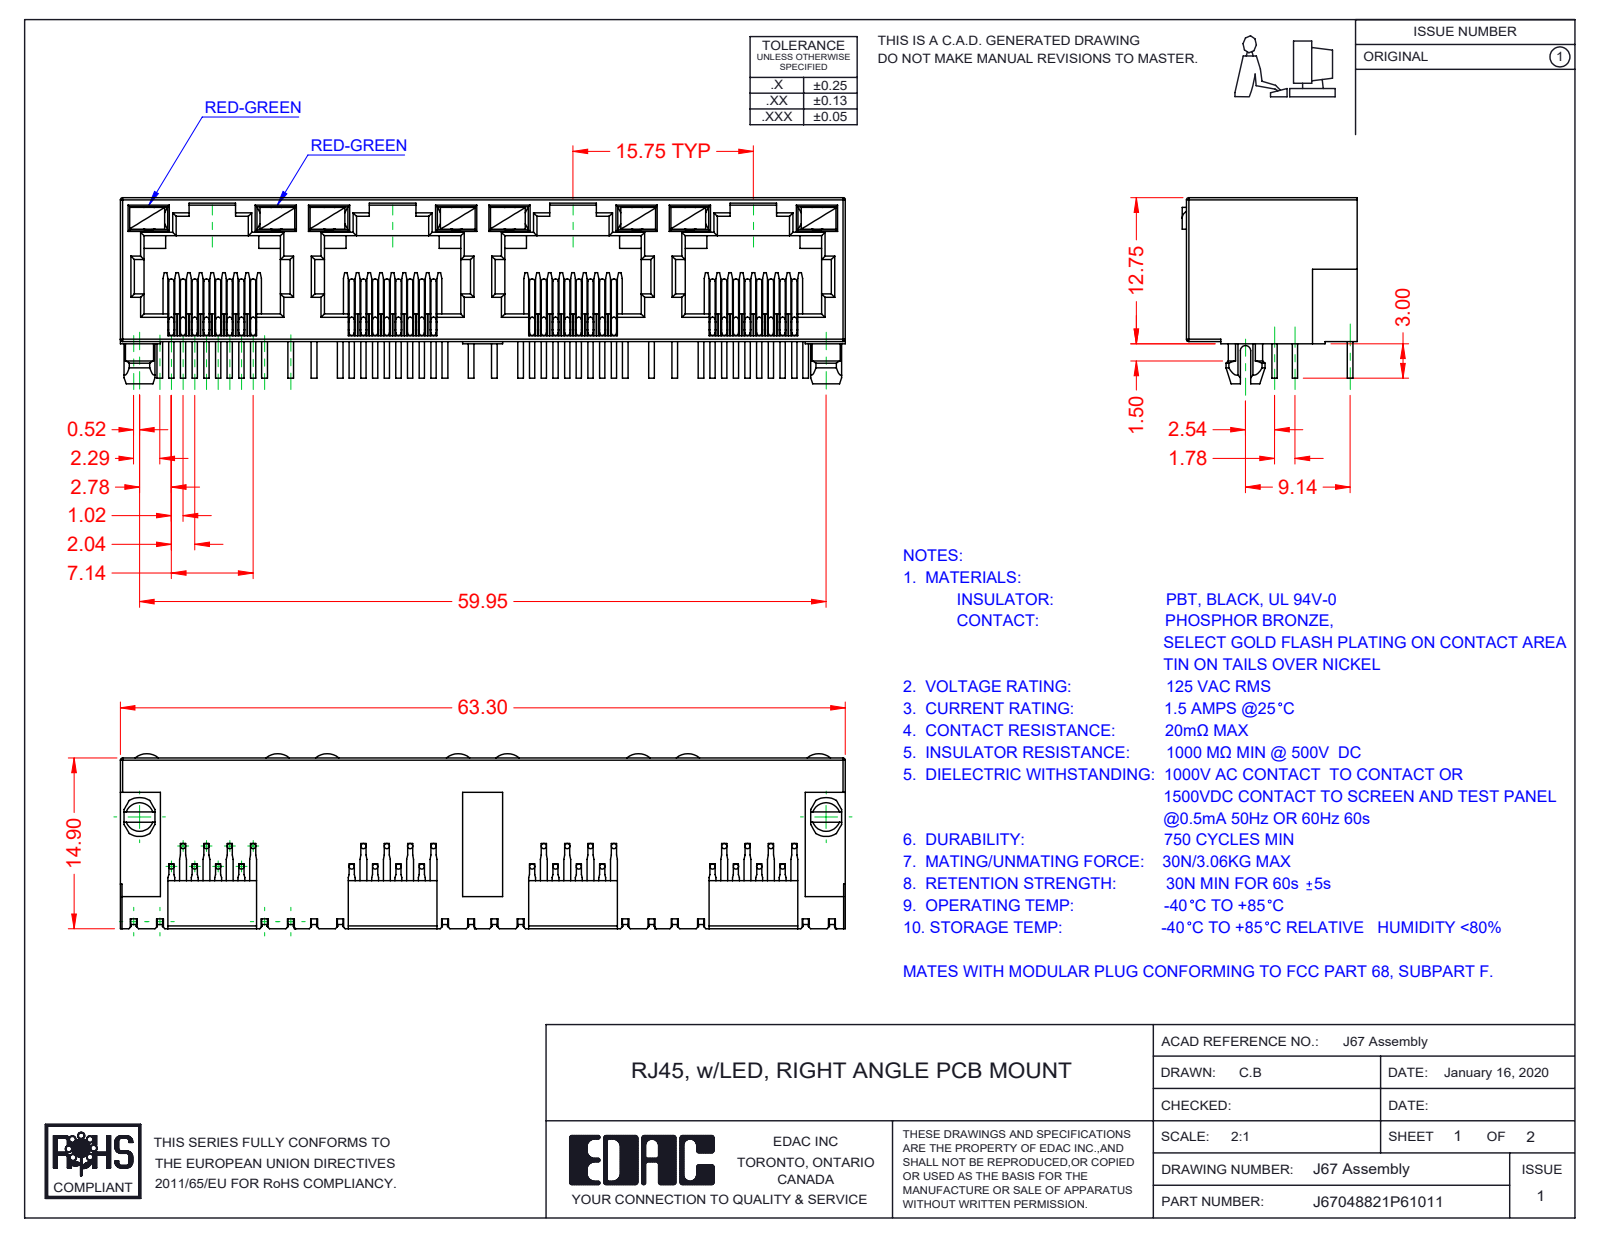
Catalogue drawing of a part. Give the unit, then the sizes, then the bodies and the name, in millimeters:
Units: millimetres
Overall size (bounding box): 63.3 × 16.25 × 15.28
Round bosses / shafts (diameter × count): ⌀0.46 ×96
Partial cylindrical surfaces — rounded edges, fillets, slot ends (radius × count): R0.2 ×66, R0.3 ×29, R0.45 ×9, R1.55 ×8, R1.5 ×2, R1.7 ×2, R0.35 ×1, R1 ×1
Main face-to-face distances: 0.5, 12.55, 1.89, 0.89, 10, 15.75, 1, 1.39, 11, 11.89
Volume: 5 159 mm³ · Surface area: 11 573 mm²
Bodies: 41 solids, 2481 faces (1781 planar, 492 cylindrical, 208 other)
Part name (STEP PRODUCT): 67 LED RH_6-Red-Green; 67 Contacts; 67 LED LH_6-Red-Green; 67 Insulator (+1 more)
STEP written by: SolidWorks 2016 (CONFIG_CONTROL_DESIGN)
